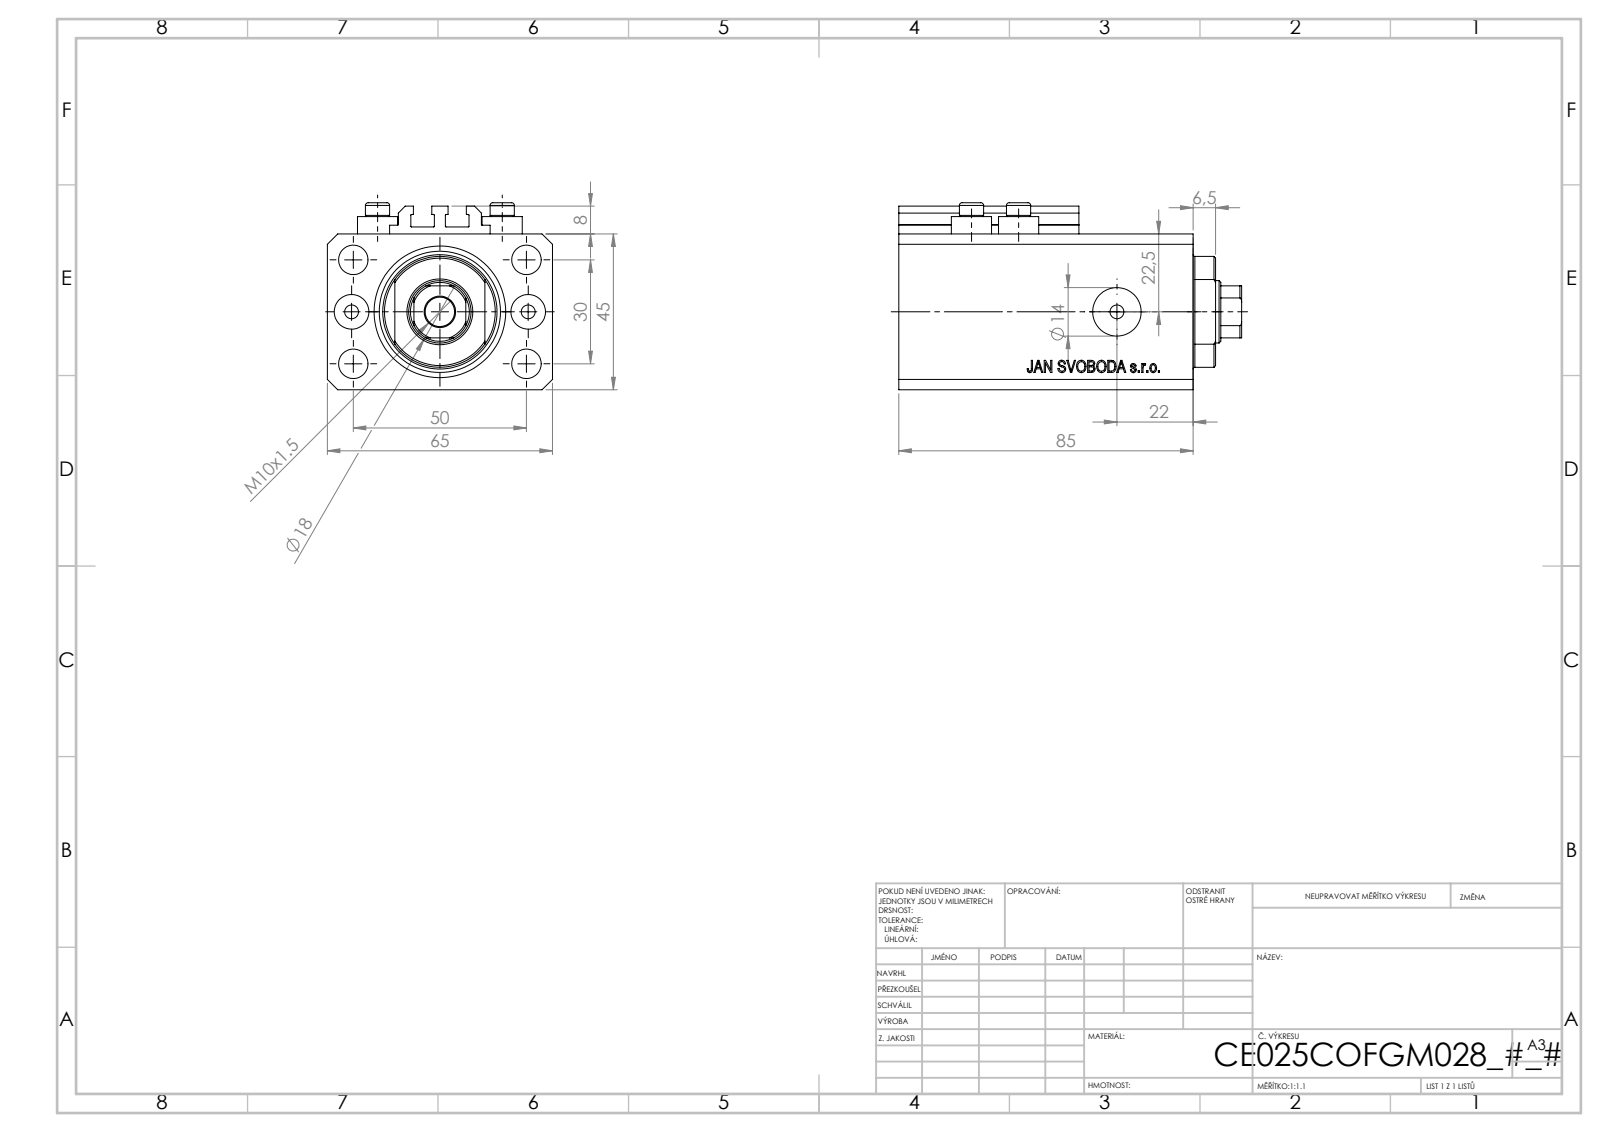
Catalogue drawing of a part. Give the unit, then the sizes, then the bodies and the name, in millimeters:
Units: millimetres
Overall size (bounding box): 99 × 65 × 54
Round holes (diameter × count): ⌀4 ×8, ⌀8.5 ×5, ⌀10 ×2, ⌀14 ×2, ⌀18 ×1, ⌀25 ×1, ⌀38 ×1
Round bosses / shafts (diameter × count): ⌀11.6 ×4, ⌀7 ×4
Partial cylindrical surfaces — rounded edges, fillets, slot ends (radius × count): R0.2 ×10, R8.5 ×1, R16 ×1
Main face-to-face distances: 45, 65, 14, 71, 85, 47, 6.9, 64.1, 78.1, 3
Hole centre spacings: 15.01, 29.15, 52.68, 13.6, 25.5, 30, 36, 38.48
Volume: 232 497 mm³ · Surface area: 61 711 mm²
Bodies: 8 solids, 1034 faces (504 planar, 86 cylindrical, 444 other)
Part name (STEP PRODUCT): V250CE_VC_C; ALLEN BOLT V250CE; V250CE_C_VCP; V250CE_C_Body
STEP written by: SolidWorks 2019 (CONFIG_CONTROL_DESIGN)
